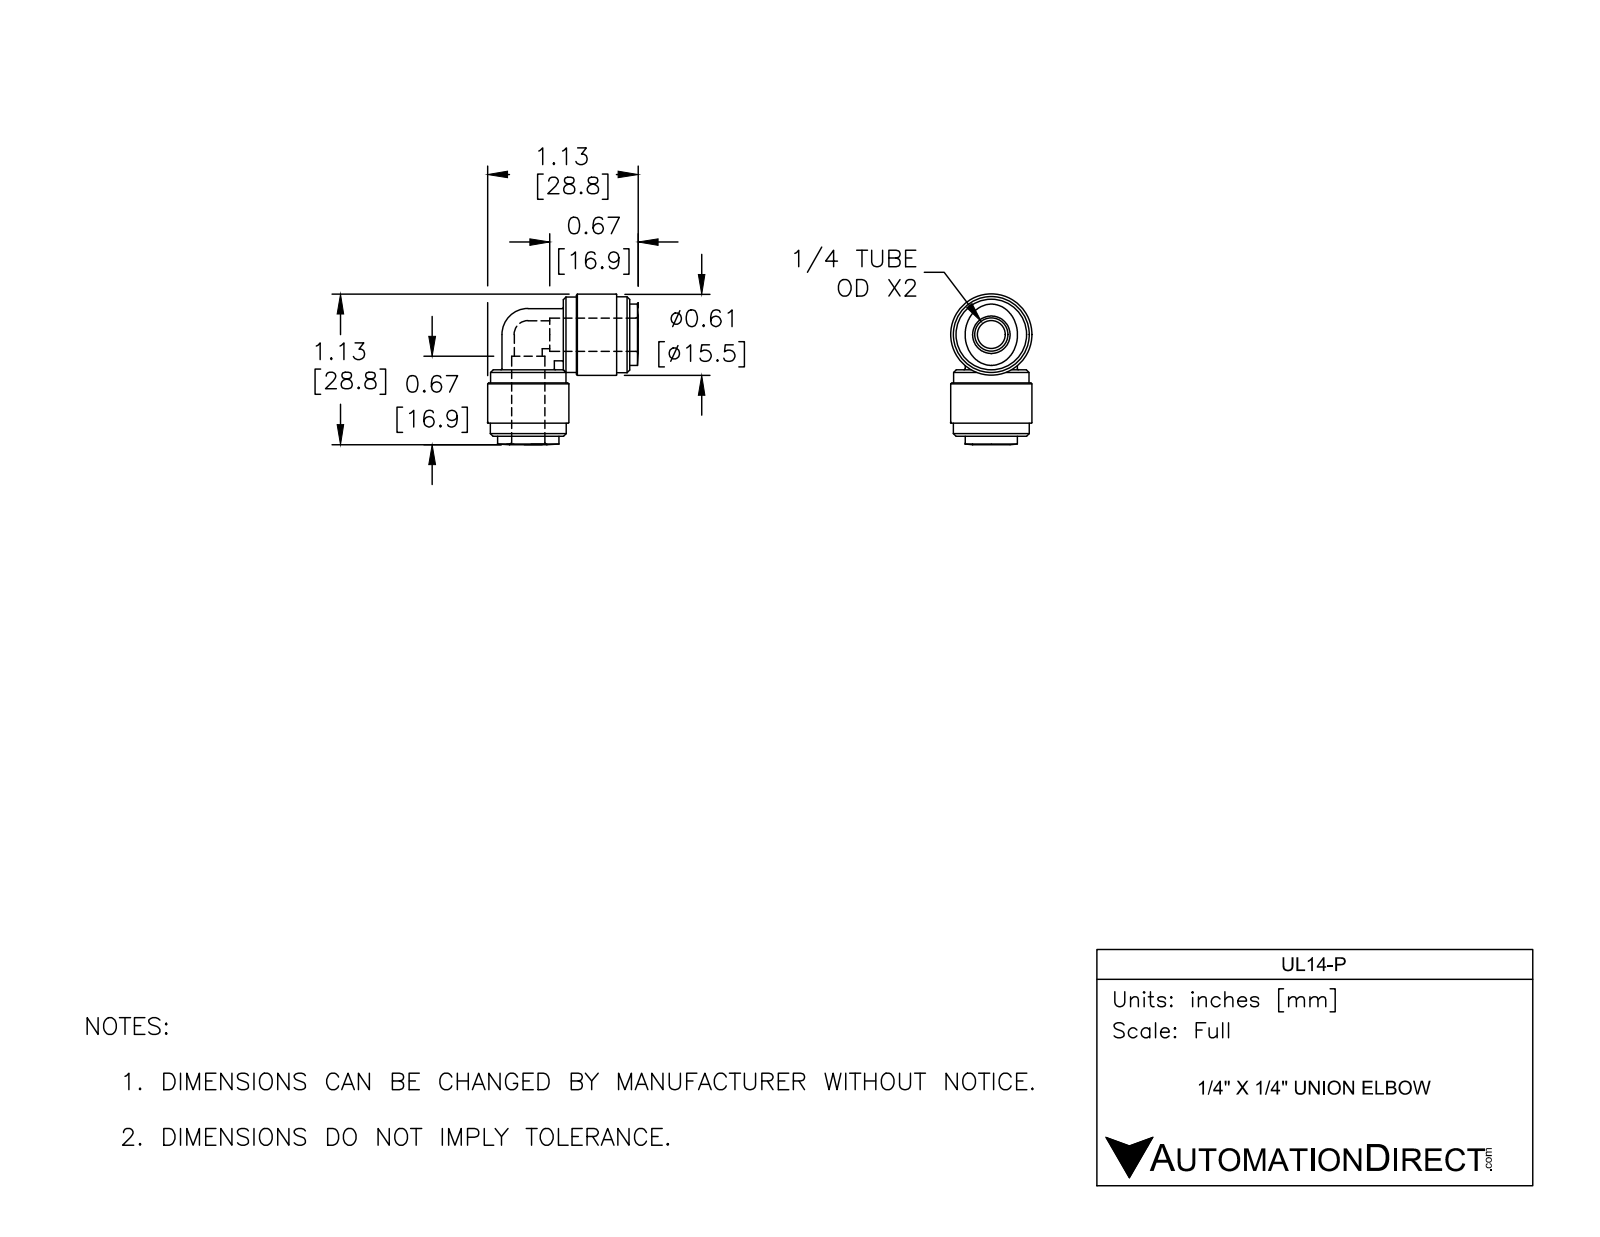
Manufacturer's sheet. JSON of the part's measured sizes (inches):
{"part_name": "UL14-P", "step_written_by": "SolidWorks 2017 (AUTOMOTIVE_DESIGN)", "units": "inches", "bodies": {"solids": 1, "faces": 70, "planar": 10, "cylindrical": 24, "other": 36}, "overall_size": [1.132, 1.132, 0.61], "volume_in3": 0.279, "surface_area_in2": 4.62, "round_holes": [[0.209, 2], [0.25, 2]], "round_bosses_or_shafts": [[0.61, 2], [0.571, 2], [0.567, 2], [0.394, 2]], "face_to_face_distances": [0.5, 0.098, 0.402, 0.303, 0.602, 0.504, 0.201, 0.102]}
